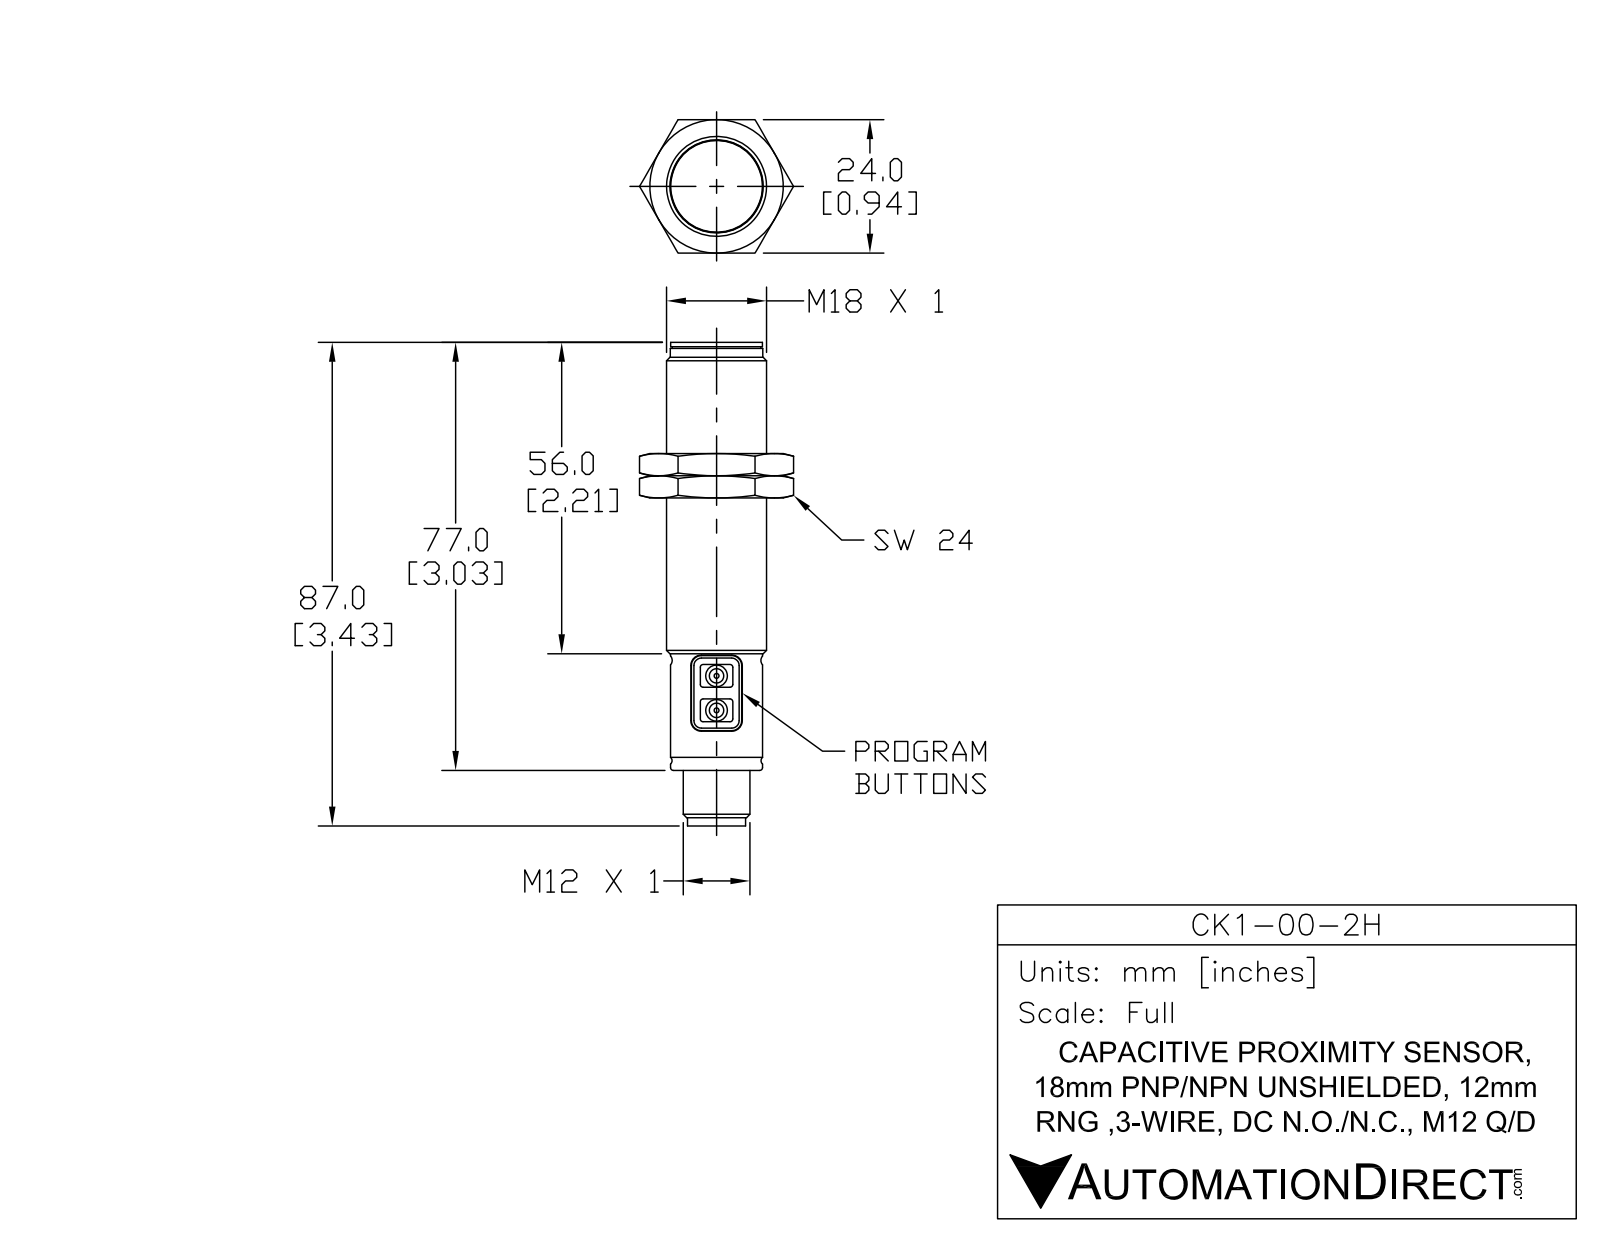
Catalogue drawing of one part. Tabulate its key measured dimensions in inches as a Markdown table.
| quantity | value |
| --- | --- |
| part name | CK1-00-2H |
| STEP written by | SolidWorks 2017 (AUTOMOTIVE_DESIGN) |
| units | inches |
| bodies | 3 solids, 147 faces (50 planar, 37 cylindrical, 60 other) |
| overall size | 3.425 × 1.091 × 0.945 |
| volume | 1.291 in³ |
| surface area | 11.58 in² |
| round holes (diameter × count) | 0.33 × 1, 0.666 × 1 |
| round bosses / shafts (diameter × count) | 0.709 × 1, 0.656 × 1, 0.652 × 1, 0.65 × 1, 0.627 × 1, 0.472 × 1, 0.411 × 1 |
| partial cylindrical surfaces (radius × count) | 0.02 × 8, 0.075 × 4, 0.031 × 2, 0.047 × 2, 0.023 × 1 |
| main face-to-face distances | 0.945, 0.157, 0.787, 0.315, 1.102, 1.929, 2.087, 2.244, 3.031, 0.047 |
